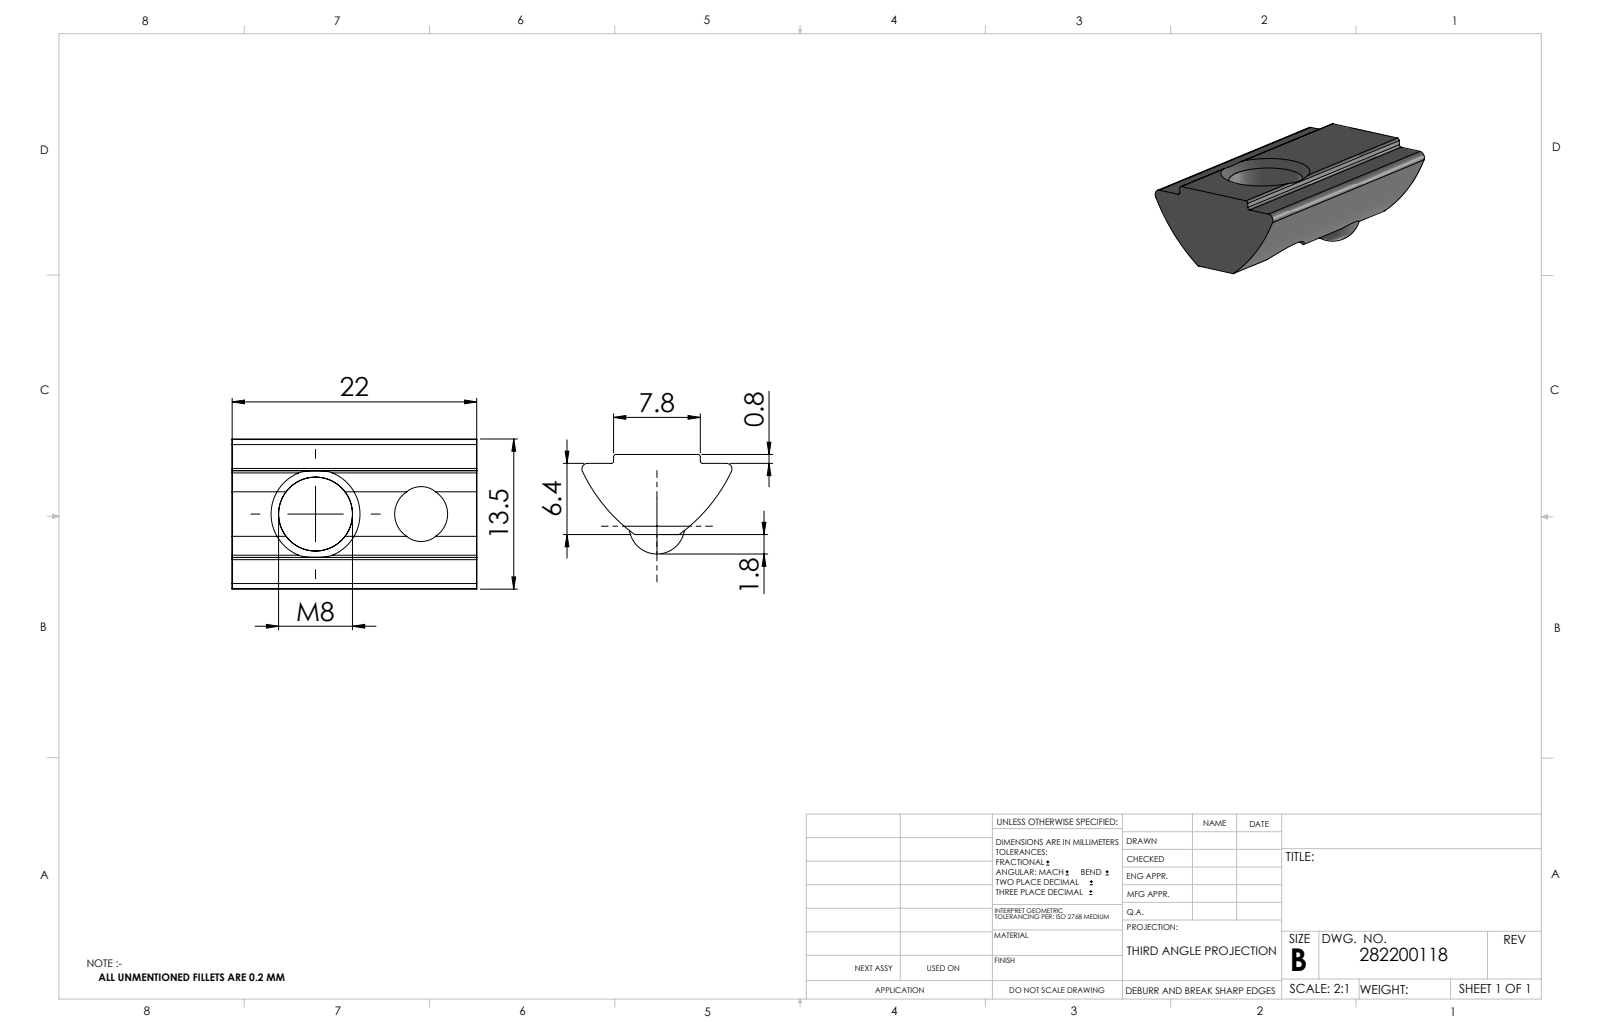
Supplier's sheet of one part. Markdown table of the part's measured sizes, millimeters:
| quantity | value |
| --- | --- |
| part name | 282200118_c_1 |
| STEP written by | SolidWorks 2014 (CONFIG_CONTROL_DESIGN) |
| units | millimeters |
| bodies | 1 solid, 25 faces (11 planar, 11 cylindrical, 3 other) |
| overall size | 22 × 13.5 × 8.9 |
| volume | 1 304 mm³ |
| surface area | 974 mm² |
| round holes (diameter × count) | 6.65 × 1 |
| partial cylindrical surfaces (radius × count) | 0.2 × 4, 0.51 × 2, 15 × 2 |
| main face-to-face distances | 0.8, 22, 6.4, 7.2, 7.8 |
